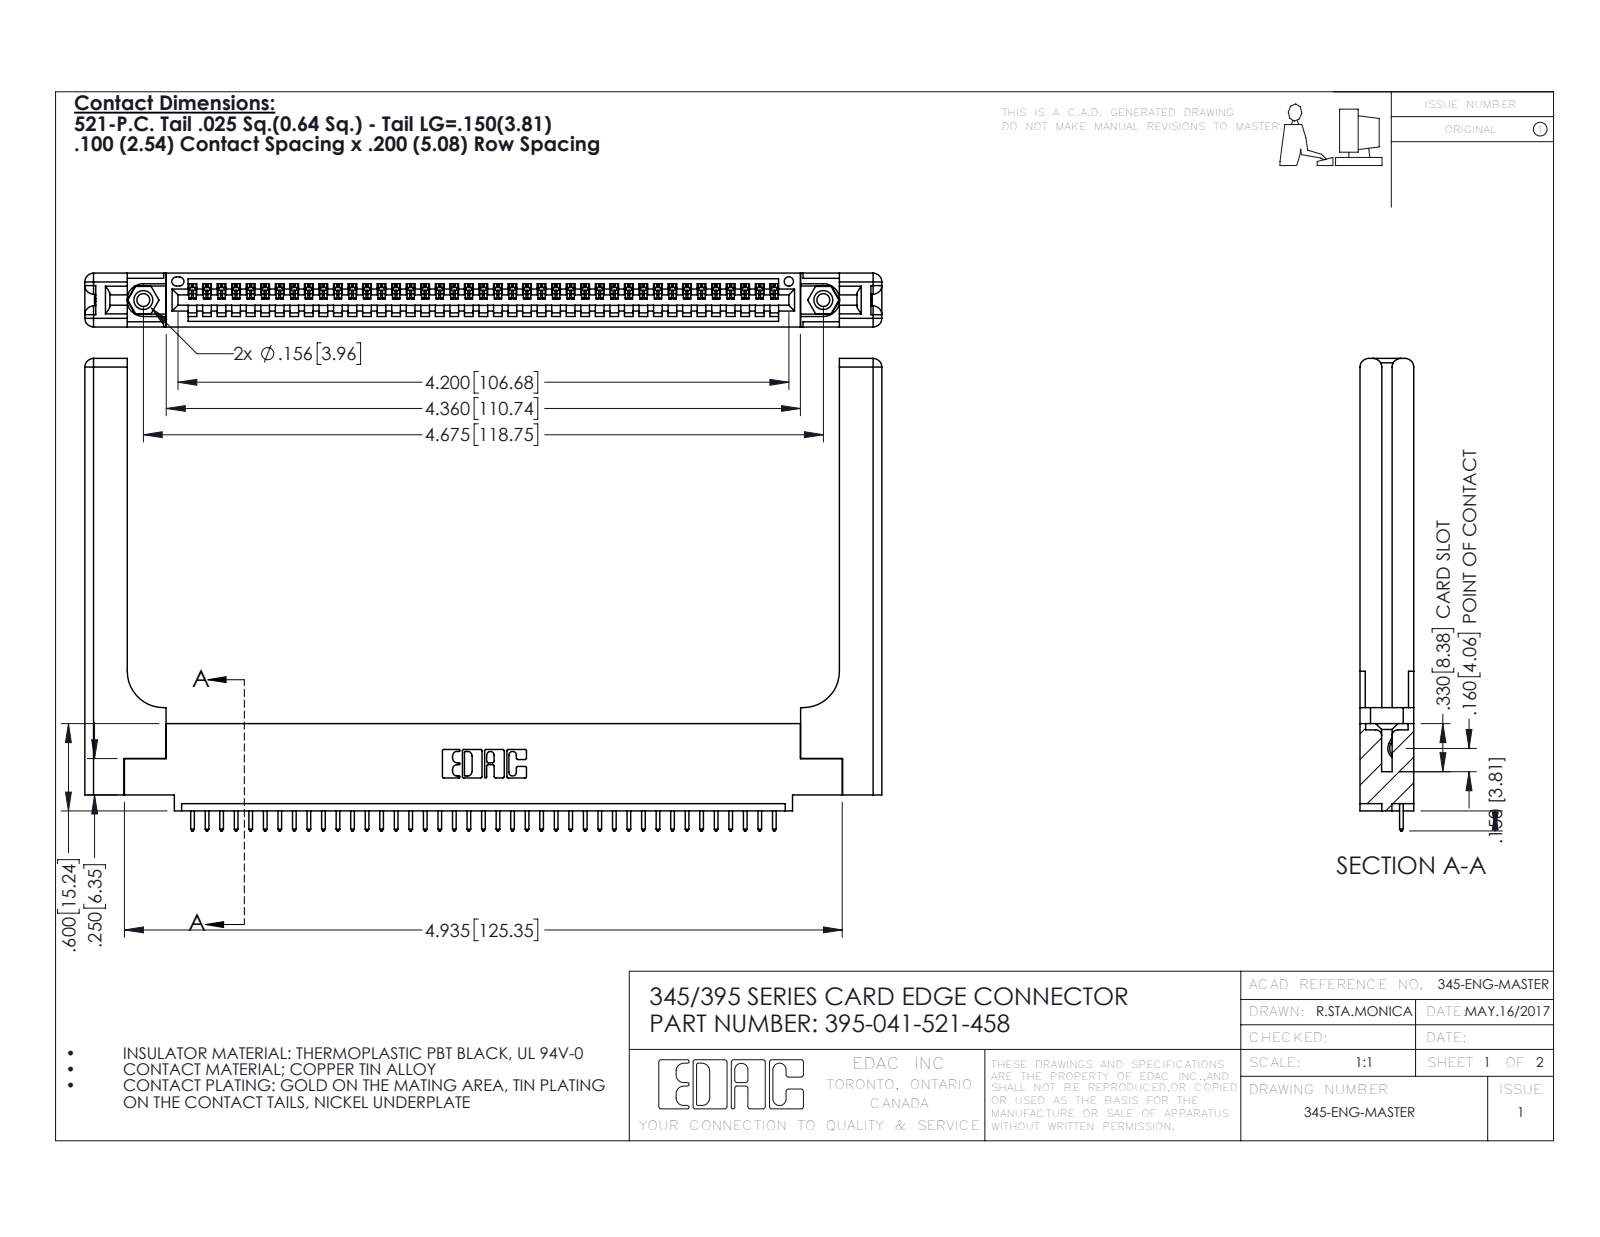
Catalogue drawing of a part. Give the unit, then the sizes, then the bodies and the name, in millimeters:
Units: millimetres
Overall size (bounding box): 139.2 × 82.5 × 9.4
Round holes (diameter × count): ⌀2.3 ×2, ⌀3.2 ×2, ⌀4 ×2, ⌀1.6 ×1
Round bosses / shafts (diameter × count): ⌀3.9 ×2
Partial cylindrical surfaces — rounded edges, fillets, slot ends (radius × count): R0.2 ×82, R0.3 ×82, R0.3 ×22, R1.5 ×16, R0.2 ×6, R0.8 ×6, R0.7 ×3, R0.8 ×2
Main face-to-face distances: 9.4, 1.8, 7.6, 5.1, 2.5, 6.9, 0.6, 3.8, 3.8, 5.7
Hole centre spacings: 6.9, 112.8, 118.7
Volume: 21 530 mm³ · Surface area: 22 220 mm²
Bodies: 46 solids, 2764 faces (1872 planar, 832 cylindrical, 60 other)
Part name (STEP PRODUCT): 395-041-521-458; 345-292-001_345-293-121; 345-220-058_345-220-058; 345-250-001_345-250-001-102 (+1 more)
STEP written by: SolidWorks 2016 (CONFIG_CONTROL_DESIGN)
